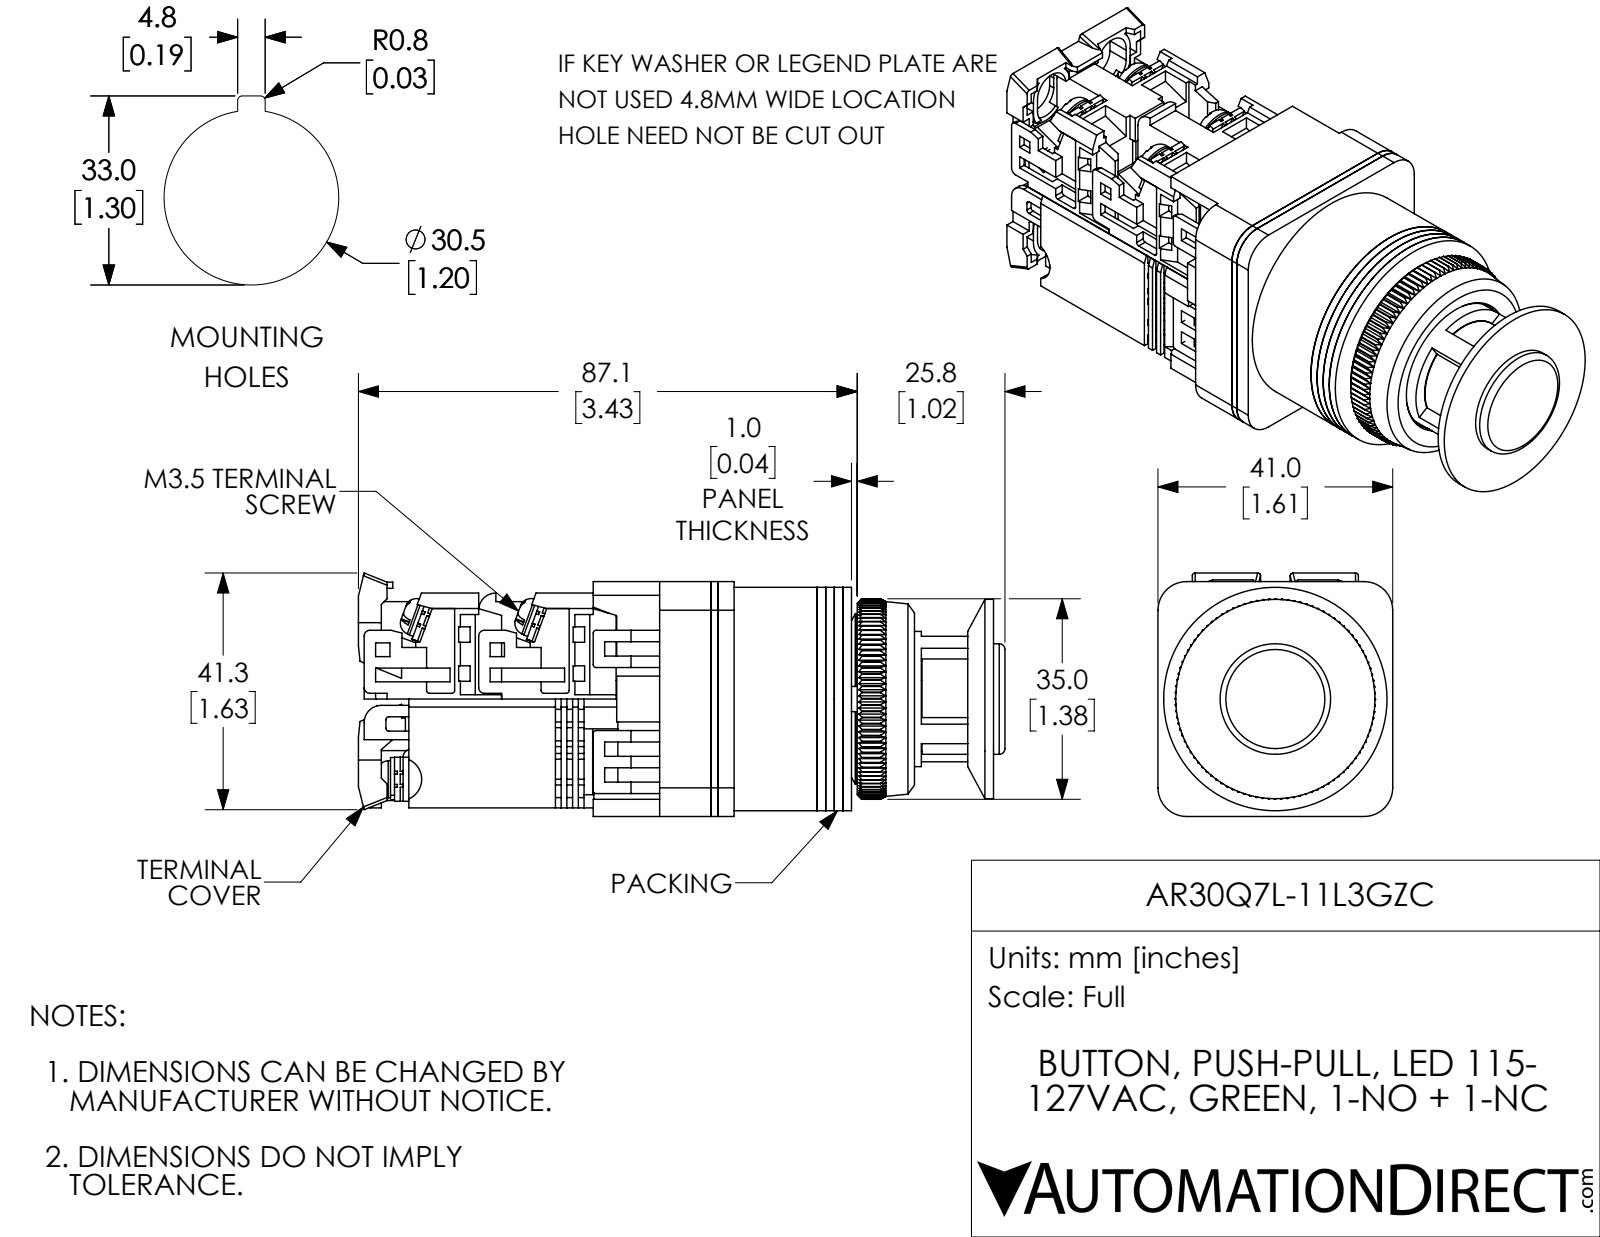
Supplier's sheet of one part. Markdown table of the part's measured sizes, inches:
| quantity | value |
| --- | --- |
| part name | AR30Q7L-11L3GZC |
| STEP written by | SolidWorks 2017 (AUTOMOTIVE_DESIGN) |
| units | inches |
| bodies | 36 solids, 2273 faces (1668 planar, 357 cylindrical, 248 other) |
| overall size | 4.445 × 1.673 × 1.614 |
| volume | 5.645 in³ |
| surface area | 93.36 in² |
| round holes (diameter × count) | 0.138 × 6, 0.142 × 6, 0.118 × 2, 0.217 × 1, 0.335 × 1, 0.453 × 1, 0.571 × 1, 0.669 × 1, 0.681 × 1, 0.76 × 1, 0.768 × 1, 0.945 × 1 |
| round bosses / shafts (diameter × count) | 0.26 × 6, 0.138 × 4, 1.535 × 1, 1.37 × 1, 1.181 × 1, 1.087 × 1, 0.929 × 1, 0.827 × 1 |
| partial cylindrical surfaces (radius × count) | 0.059 × 25, 0.02 × 21, 0.197 × 5, 0.039 × 4, 0.138 × 4, 0.177 × 4, 0.118 × 3, 0.016 × 1 |
| main face-to-face distances | 0.059, 0.047, 0.118, 0.858, 0.807, 0.177, 0.74, 0.681, 0.787, 1.614 |
| hole center spacings | 0.269, 0.579, 0.624, 0.638, 0.02, 0.583, 0.583, 0.606 |
